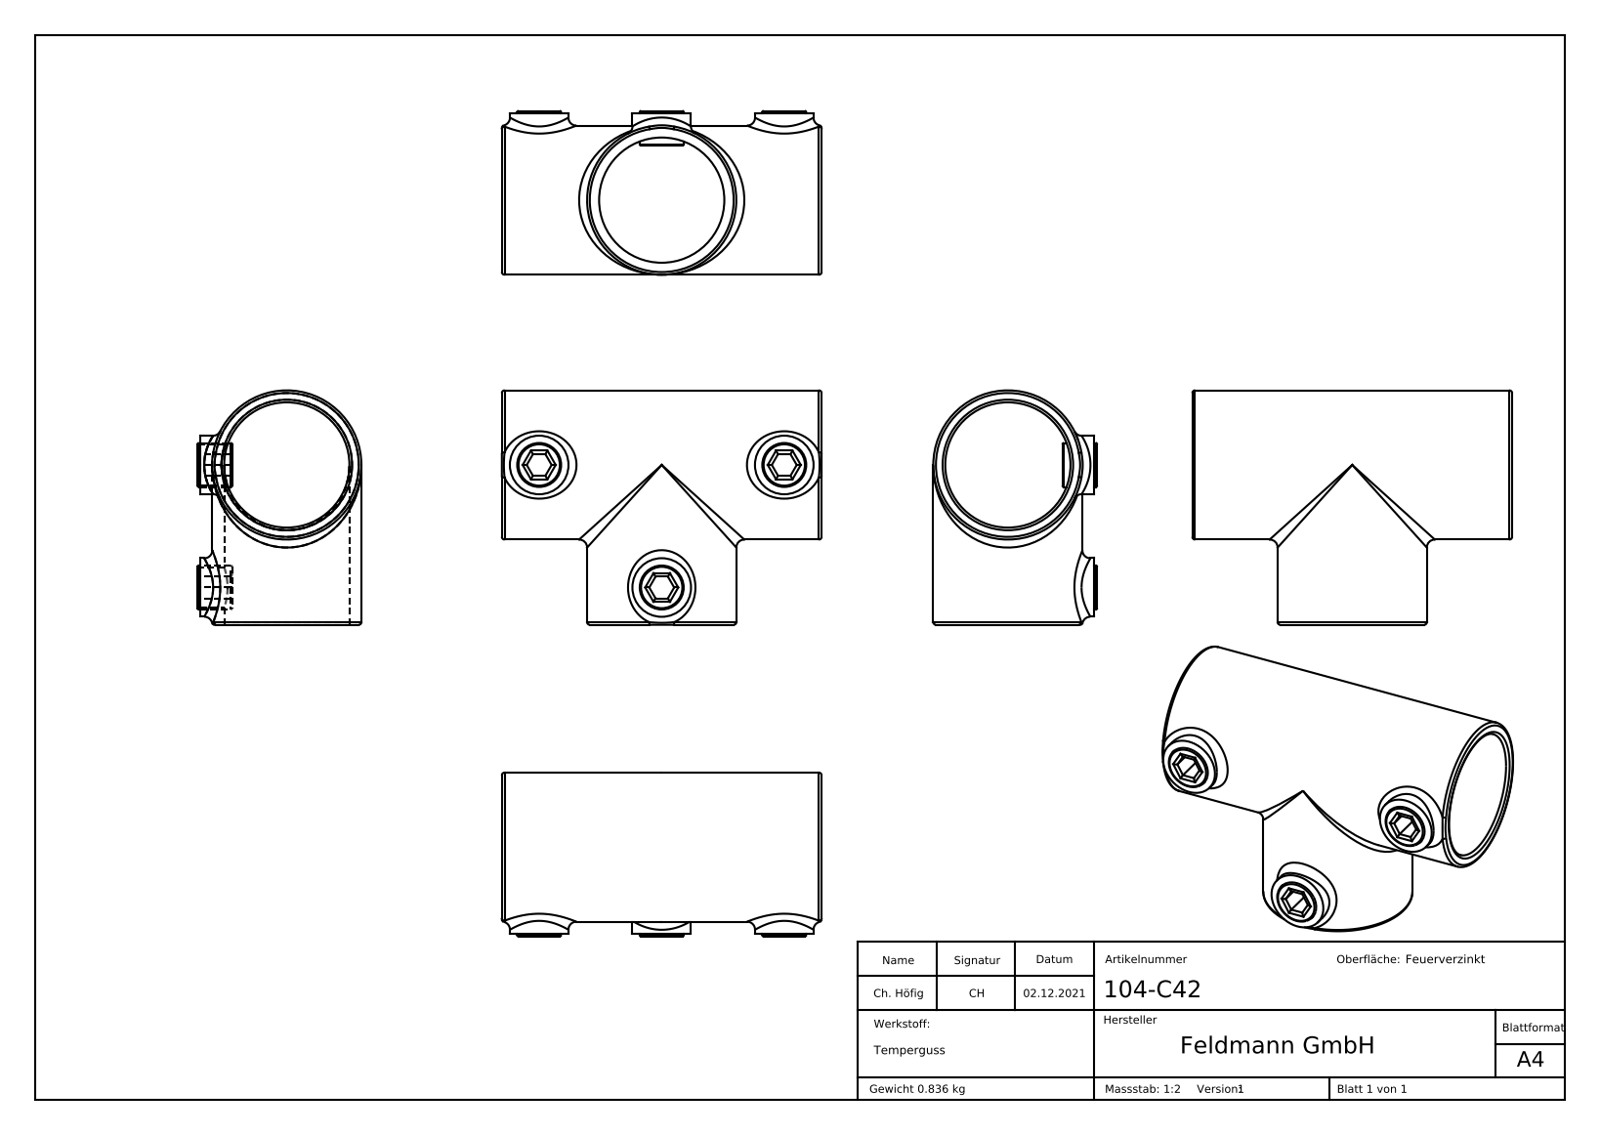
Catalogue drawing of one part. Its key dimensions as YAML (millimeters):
part_name: "104-C42 Teil1; 104-C42 Teil2; 104-C42"
step_written_by: "SolidWorks 2018 (CONFIG_CONTROL_DESIGN)"
units: millimeters
bodies: {solids: 4, faces: 102, planar: 30, cylindrical: 49, other: 23}
overall_size: [120, 88, 61.5]
volume: 114034
surface_area: 54444
round_holes:
  - {diameter: 15.25, count: 3}
  - {diameter: 47, count: 2}
round_bosses_or_shafts:
  - {diameter: 22, count: 3}
  - {diameter: 16.5, count: 3}
  - {diameter: 56, count: 2}
partial_cylinders:
  - {radius: 2, count: 32}
face_to_face_distances: [120, 8.1, 1, 12, 13, 79.67, 8.09, 55.95, 24.93, 54.74]
hole_center_spacings: [65.05, 92]
